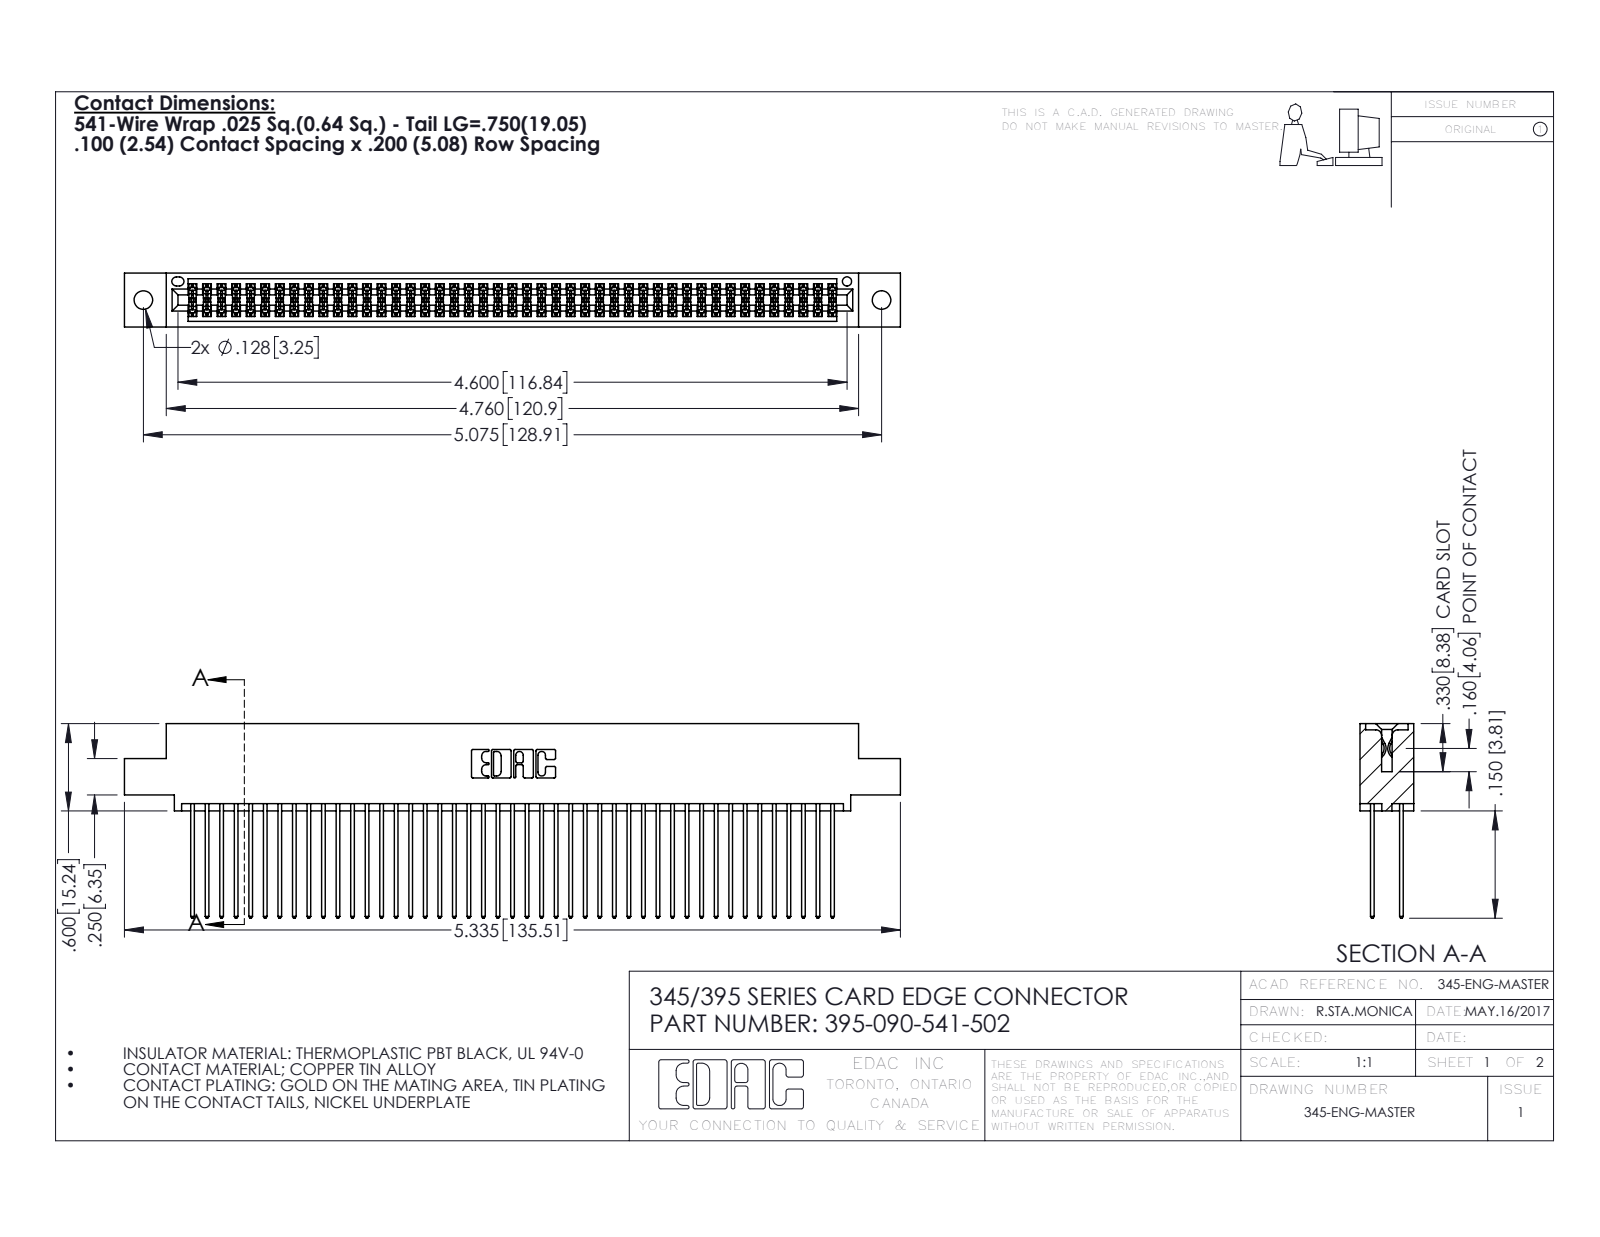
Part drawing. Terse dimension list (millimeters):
name: 395-090-541-502; 345 Part_0.110 Offset - 0.128 Dia; 345-292-001_345-293-141
written by: SolidWorks 2016 (CONFIG_CONTROL_DESIGN)
unit: mm
bodies: 91 solids, 4630 faces (3054 planar, 1576 cylindrical, 0 other)
size: 135.5 × 34 × 9.4
volume: 13 600 mm³; area: 22 410 mm²
holes: 2× ⌀3.3, 1× ⌀1.6
rounds: 135× R0.2, 90× R0.3, 22× R0.3, 6× R0.2, 6× R0.8, 3× R0.7, 2× R0.4, 2× R0.5
face distances: 7.6, 1.8, 5.1, 2.5, 6.9, 0.6, 5.7, 9.4, 4.4, 3.8
hole spacings: 6.9, 122.9, 128.9
